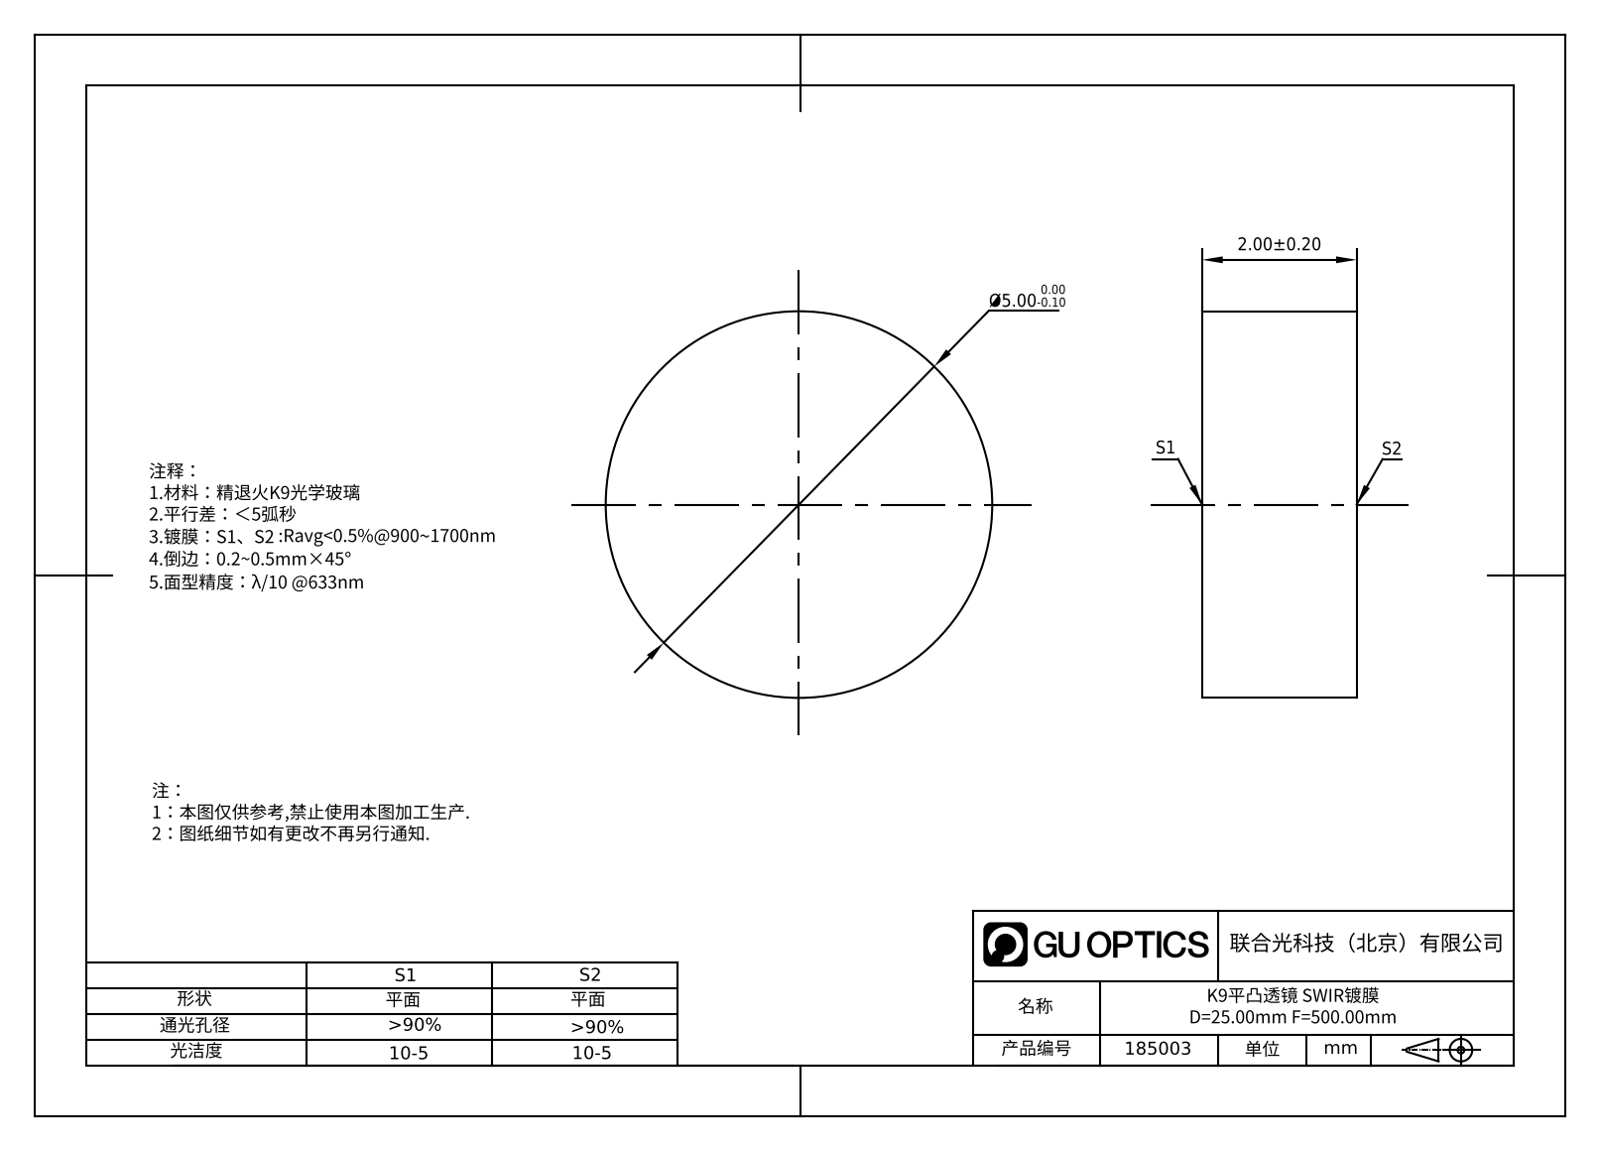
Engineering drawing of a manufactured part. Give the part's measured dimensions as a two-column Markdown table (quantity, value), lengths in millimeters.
| quantity | value |
| --- | --- |
| part name | 185003 |
| STEP written by | SolidWorks 2016 (AUTOMOTIVE_DESIGN) |
| units | millimeters |
| bodies | 1 solid, 4 faces (2 planar, 2 cylindrical, 0 other) |
| overall size | 12.7 × 12.7 × 3 |
| volume | 380 mm³ |
| surface area | 373 mm² |
| round bosses / shafts (diameter × count) | 12.7 × 1 |
| main face-to-face distances | 3 |
